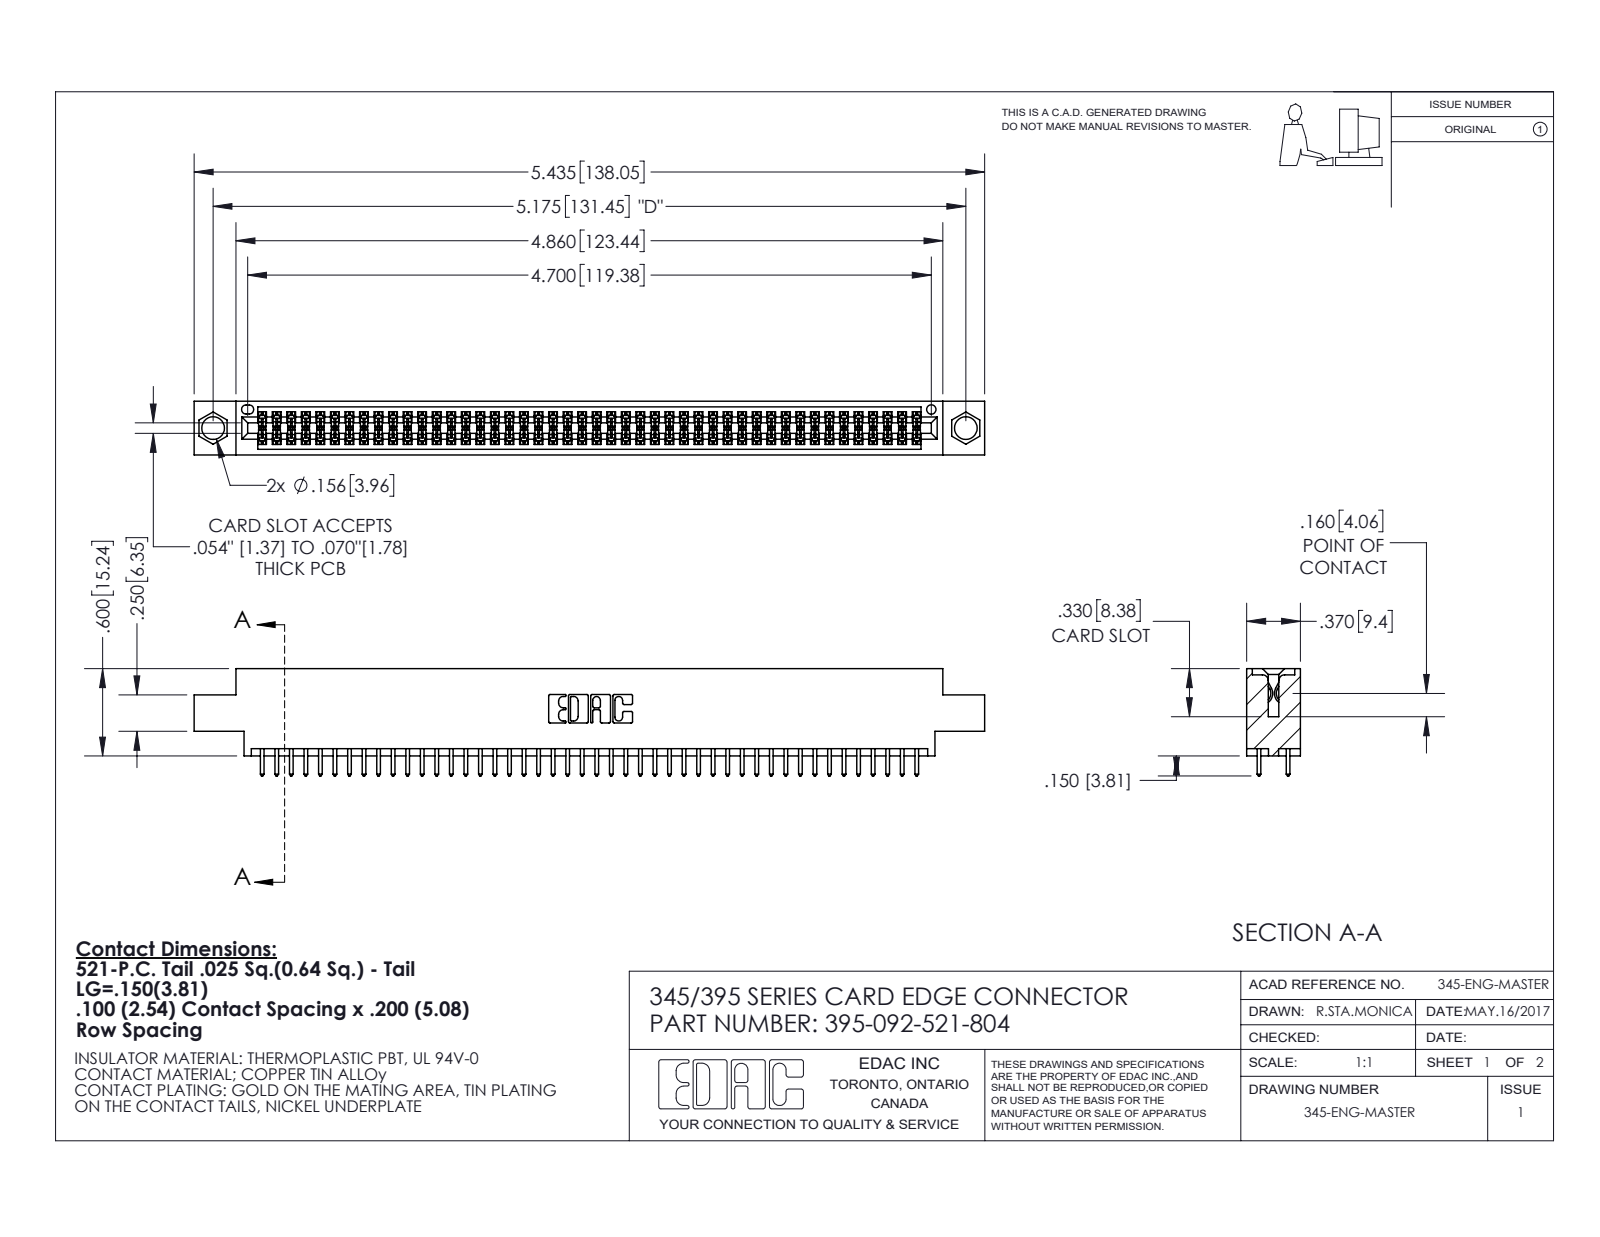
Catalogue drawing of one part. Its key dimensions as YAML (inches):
part_name: "345-292-001_345-293-121; 395-092-521-804; 345 Part_0.170 Offset - 0.156 Dia-TI"
step_written_by: "SolidWorks 2020 (CONFIG_CONTROL_DESIGN)"
units: inches
bodies: {solids: 93, faces: 4744, planar: 3134, cylindrical: 1610, other: 0}
overall_size: [5.435, 0.737, 0.37]
volume: 0.805
surface_area: 29.96
round_holes:
  - {diameter: 0.156, count: 2}
  - {diameter: 0.064, count: 1}
partial_cylinders:
  - {radius: 0.006, count: 184}
  - {radius: 0.01, count: 92}
  - {radius: 0.01, count: 22}
  - {radius: 0.007, count: 6}
  - {radius: 0.031, count: 6}
  - {radius: 0.026, count: 3}
  - {radius: 0.014, count: 2}
  - {radius: 0.019, count: 2}
face_to_face_distances: [0.072, 0.298, 0.2, 0.37, 0.098, 0.272, 0.025, 0.225, 0.175, 0.149]
hole_center_spacings: [0.27, 4.939, 5.175]
